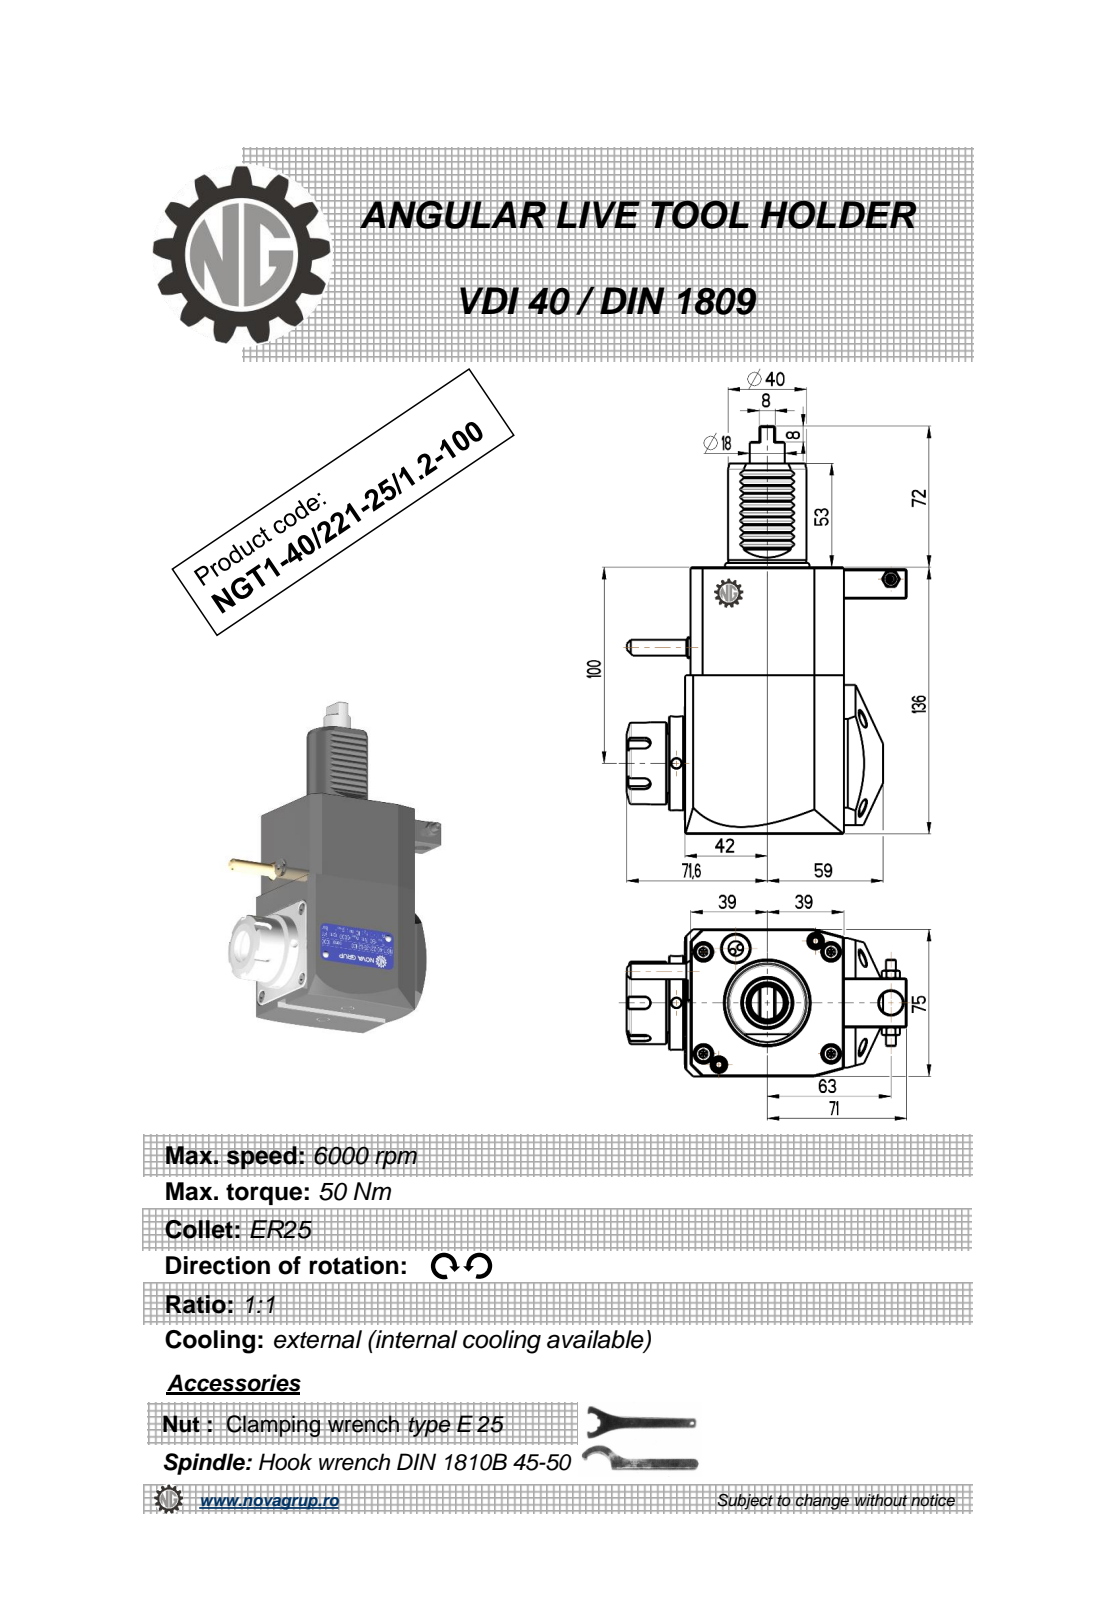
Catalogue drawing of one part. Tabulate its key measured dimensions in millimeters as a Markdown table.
| quantity | value |
| --- | --- |
| part name | NGT1_40_221_25_1_2_100 |
| STEP written by | PRO/ENGINEER BY PARAMETRIC TECHNOLOGY CORPORATION, 2010280 (CONFIG_CONTROL_DESIGN) |
| units | millimeters |
| bodies | 1 solid, 428 faces (190 planar, 89 cylindrical, 149 other) |
| overall size | 208 × 142.6 × 76.6 |
| volume | 969 601 mm³ |
| surface area | 75 077 mm² |
| round holes (diameter × count) | 5 × 3, 3 × 1, 4.2 × 1, 9.5 × 1, 12 × 1, 20.3 × 1 |
| round bosses / shafts (diameter × count) | 48 × 1, 42 × 1, 40 × 1, 37.5 × 1, 33 × 1, 17.8 × 1, 11.2 × 1, 8.96 × 1 |
| partial cylindrical surfaces (radius × count) | 0.26 × 12, 0.3 × 10, 0.22 × 6, 3 × 5, 0.8 × 2, 0.5 × 1, 40 × 1 |
| main face-to-face distances | 75, 136, 78, 81, 3, 2.8, 80.8, 8, 11, 7.5 |
| hole center spacings | 37.12, 61.13, 92.5, 109.25, 144.12 |
